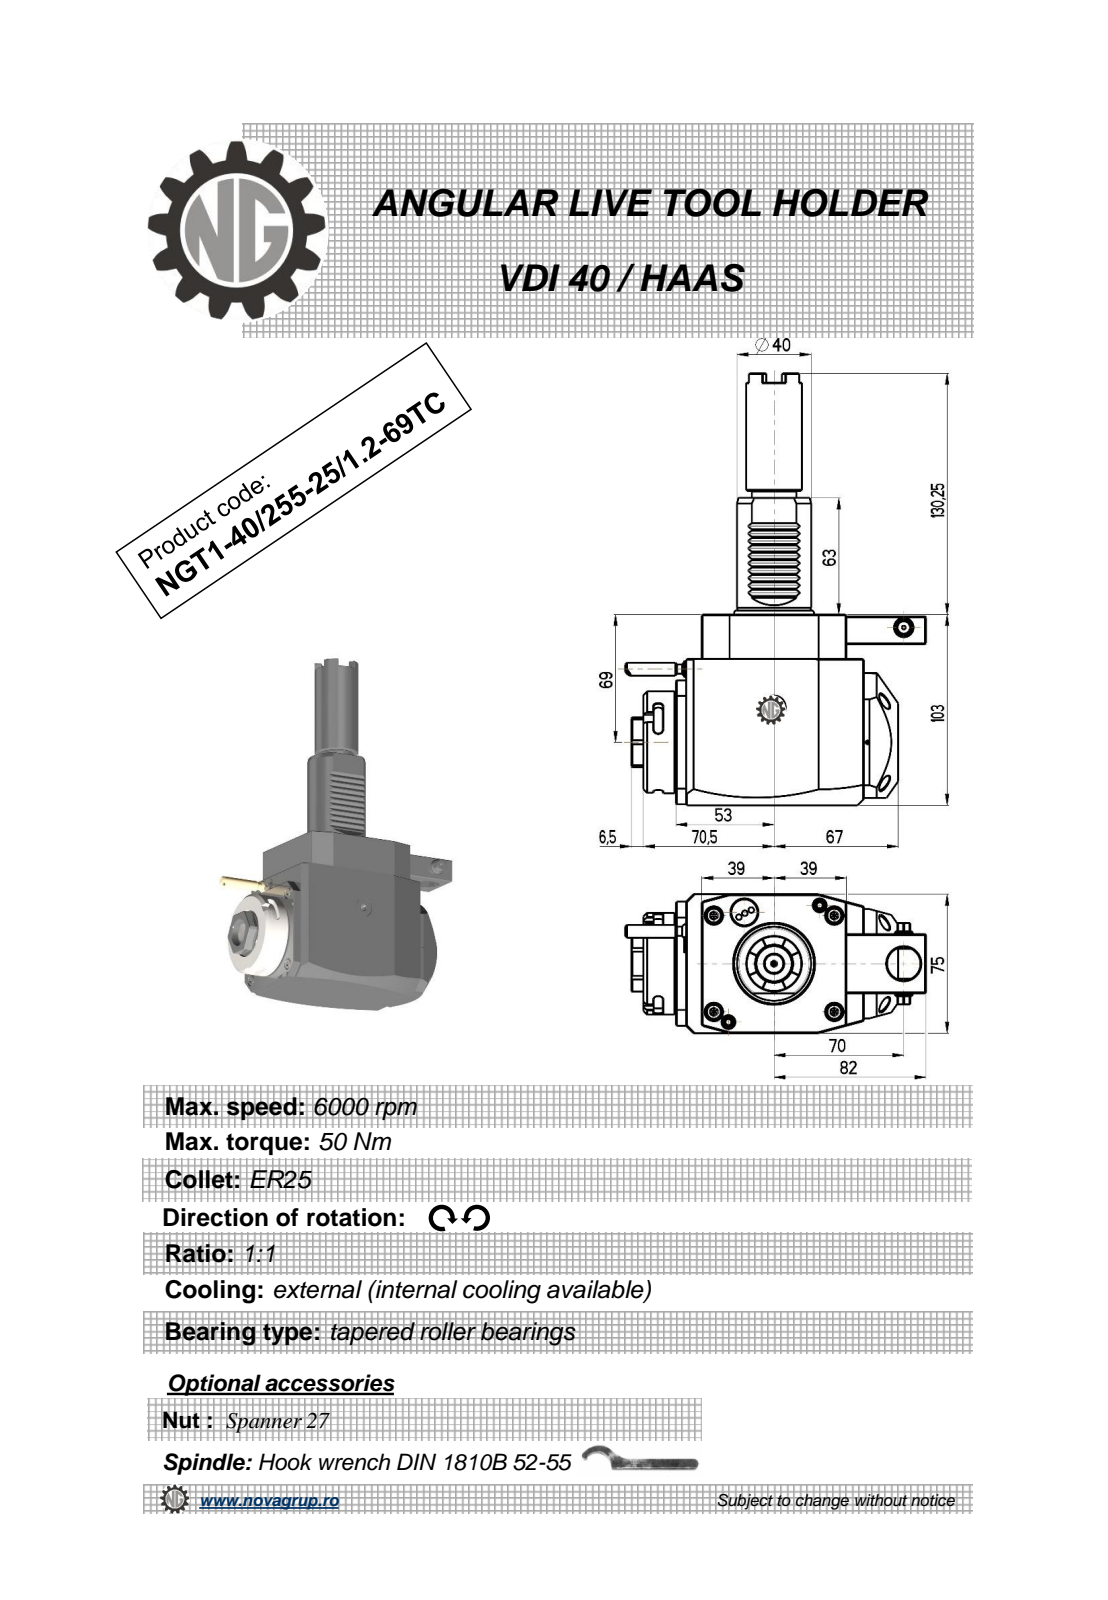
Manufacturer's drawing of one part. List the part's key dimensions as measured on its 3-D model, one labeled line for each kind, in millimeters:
Part name (STEP PRODUCT): NGT1_40_255_25_1_2_69TC
STEP written by: PRO/ENGINEER BY PARAMETRIC TECHNOLOGY CORPORATION, 2010280 (CONFIG_CONTROL_DESIGN)
Units: millimetres
Bodies: 1 solid, 387 faces (213 planar, 86 cylindrical, 88 other)
Overall size (bounding box): 233.25 × 162.33 × 75
Volume: 940 370 mm³ · Surface area: 76 636 mm²
Round holes (diameter × count): ⌀18 ×2, ⌀2 ×1, ⌀2.5 ×1, ⌀3 ×1, ⌀9.5 ×1, ⌀20 ×1
Round bosses / shafts (diameter × count): ⌀8.96 ×2, ⌀55 ×1, ⌀48 ×1, ⌀40 ×1, ⌀30 ×1, ⌀24 ×1, ⌀10 ×1, ⌀7 ×1
Partial cylindrical surfaces — rounded edges, fillets, slot ends (radius × count): R0.3 ×10, R2.5 ×6, R180 ×2, R0.5 ×1, R3.85 ×1, R4.25 ×1, R15 ×1, R24.5 ×1
Main face-to-face distances: 75, 103, 17.5, 23, 79, 102, 24, 31.5, 14, 87
Hole centre spacings: 28.11, 43.2, 61.5, 70
